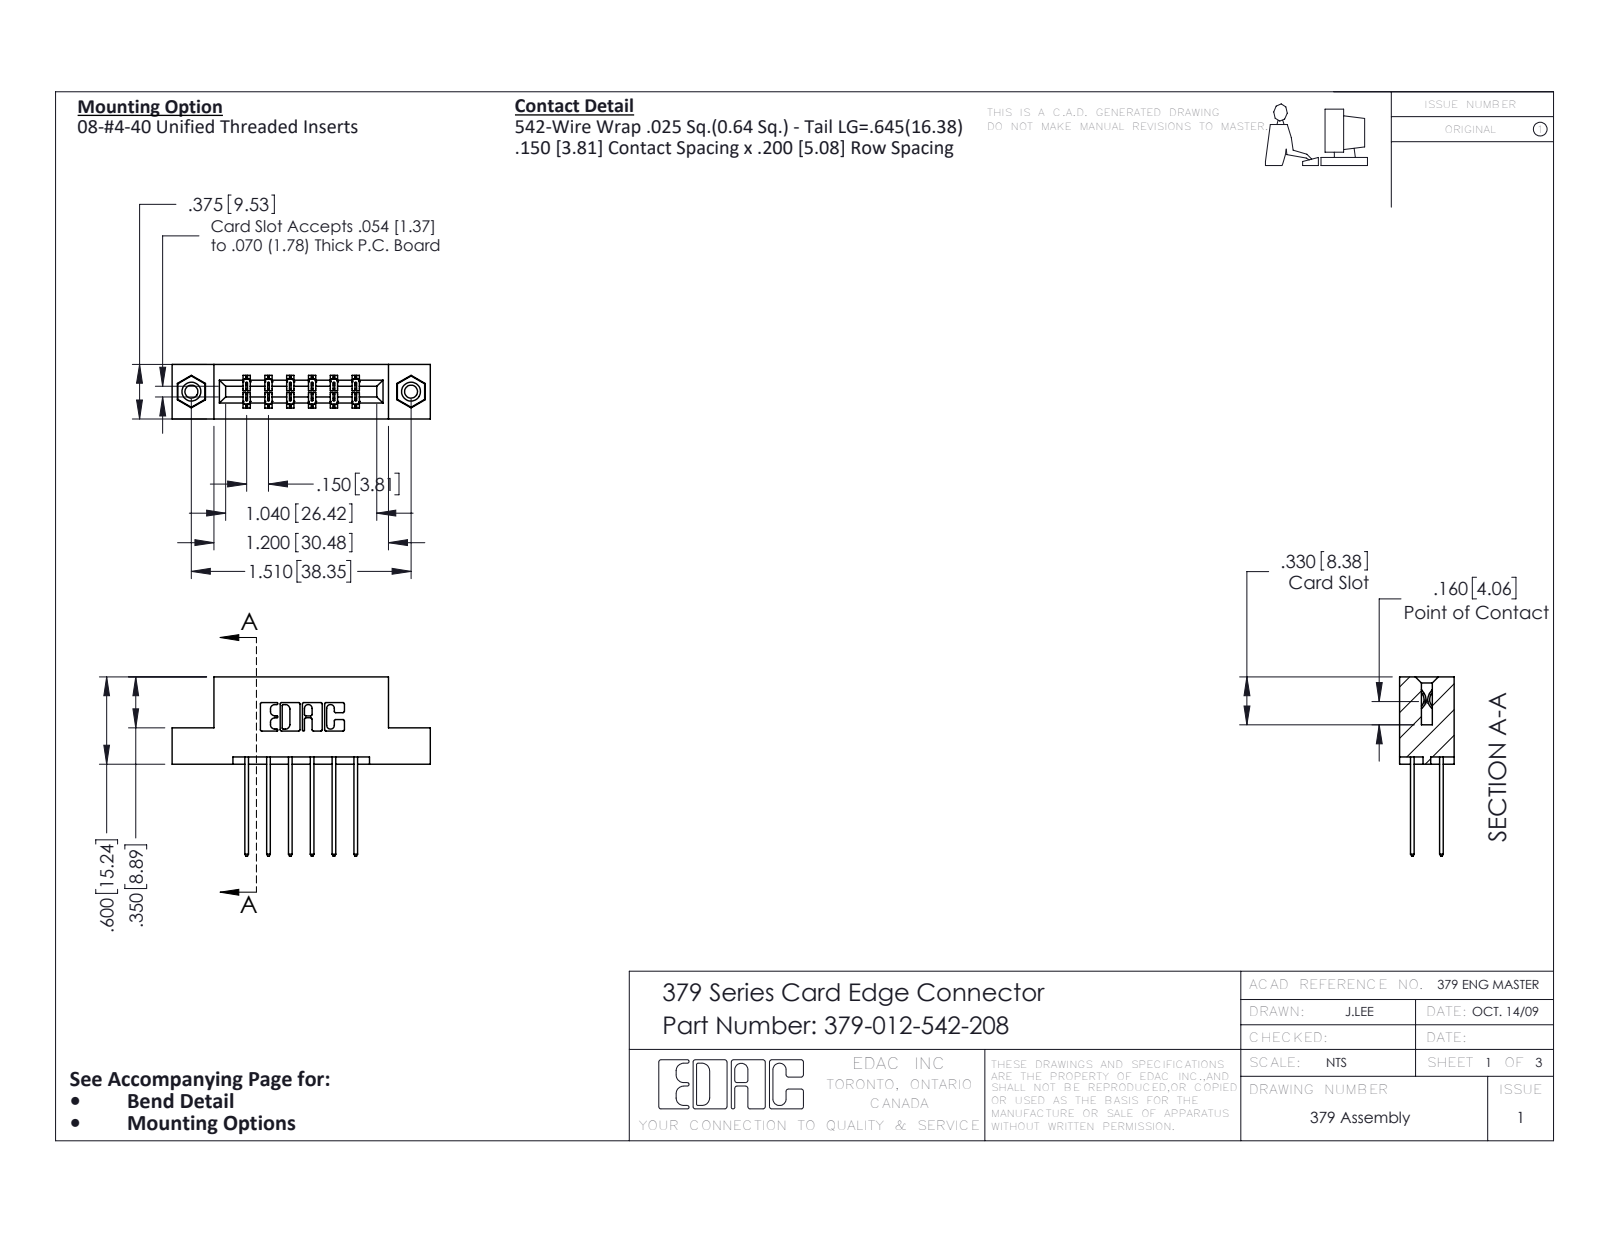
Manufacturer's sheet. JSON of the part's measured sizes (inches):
{"part_name": "345-292-001_345-293-142; 379-012-542-208; 345-250-001_345-250-003-102; 379 Part_Flush - .156 Dia - TI", "step_written_by": "SolidWorks 2016 (CONFIG_CONTROL_DESIGN)", "units": "inches", "bodies": {"solids": 15, "faces": 798, "planar": 534, "cylindrical": 248, "other": 16}, "overall_size": [1.775, 1.232, 0.375], "volume_in3": 0.268, "surface_area_in2": 7.611, "round_holes": [[0.089, 2], [0.125, 2], [0.156, 2]], "round_bosses_or_shafts": [[0.155, 2]], "partial_cylinders_radius": [[0.01, 22], [0.006, 18], [0.01, 12], [0.007, 6], [0.031, 6], [0.026, 3], [0.014, 2], [0.022, 2]], "face_to_face_distances": [0.3, 0.2, 0.15, 0.1, 0.375, 0.05, 0.075, 0.25, 0.35, 0.55], "hole_center_spacings": [1.51]}
